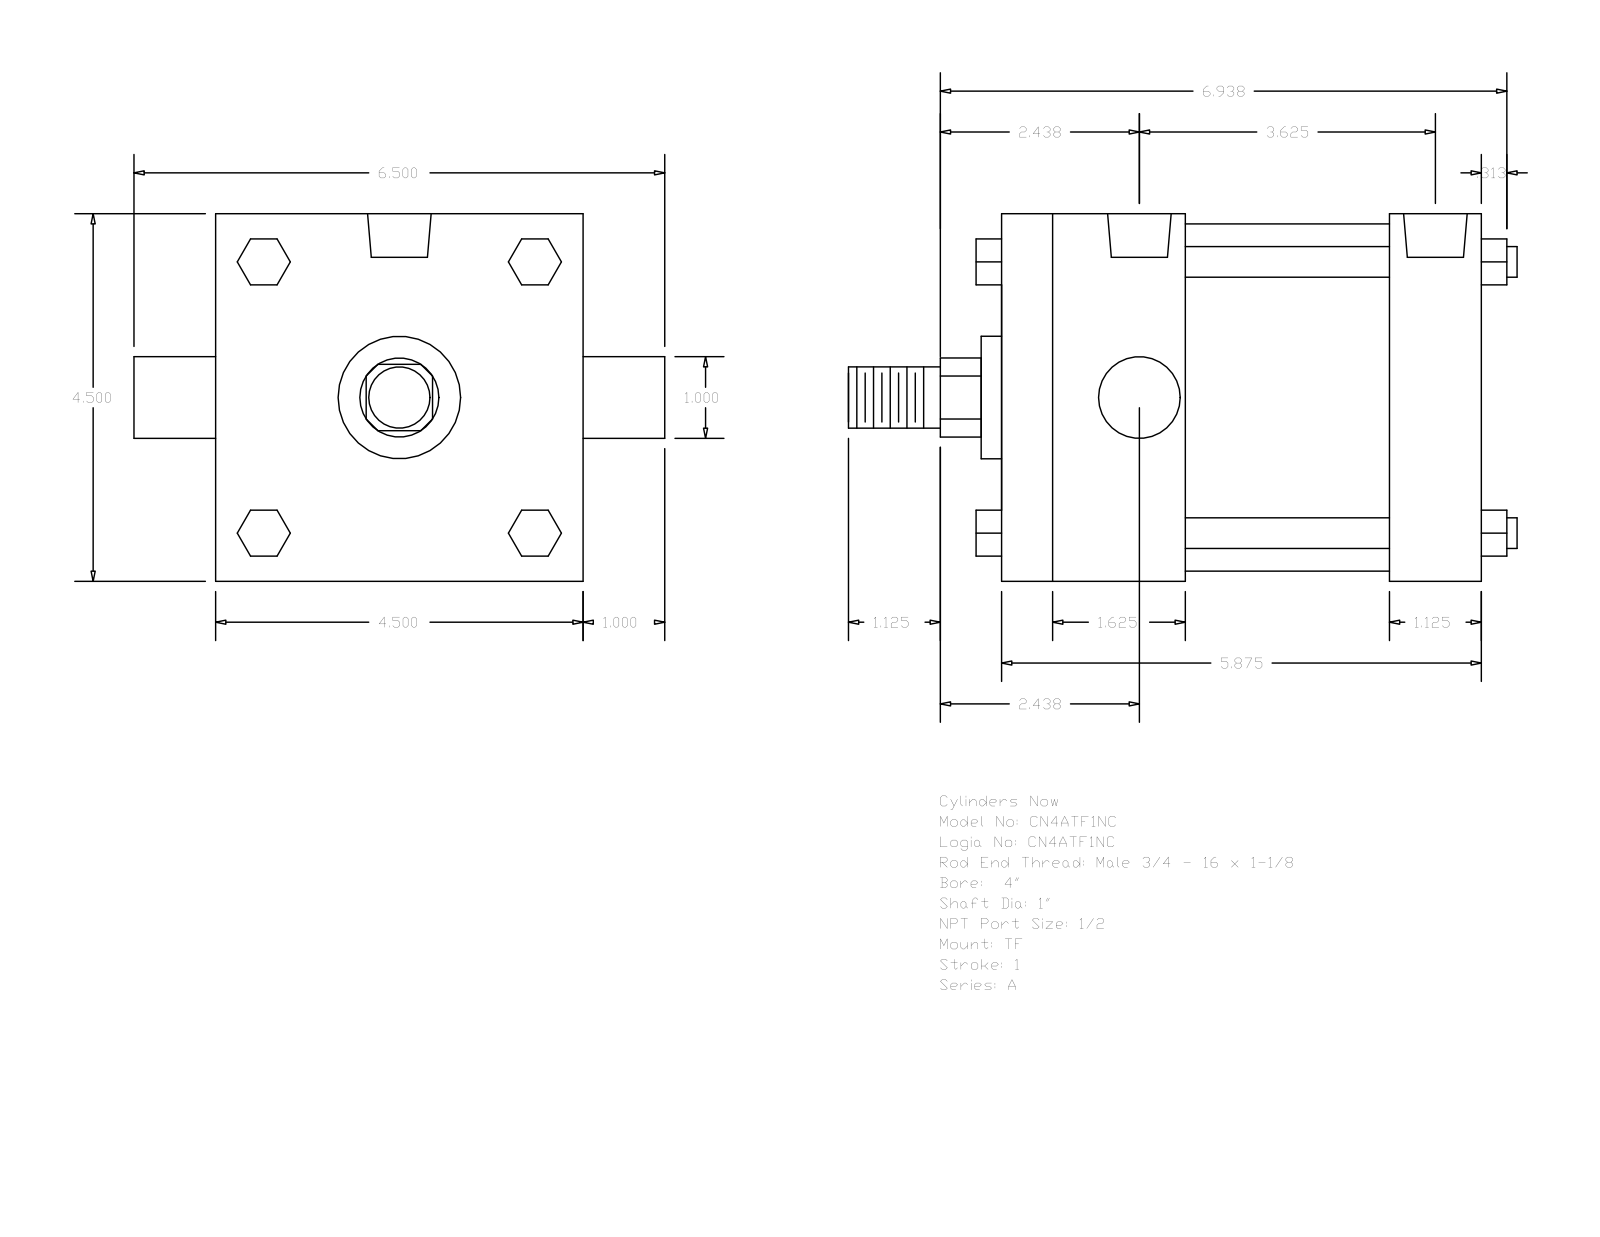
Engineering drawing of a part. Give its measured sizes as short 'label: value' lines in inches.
name: A_TF__0400_1
written by: GSSL Pune (CONFIG_CONTROL_DESIGN)
unit: in
bodies: 0 solids, 120 faces (92 planar, 28 cylindrical, 0 other)
size: 8.187 × 6.5 × 4.5
holes: 3× ⌀0.344, 2× ⌀0.778
bosses: 4× ⌀0.375, 2× ⌀1, 1× ⌀4.25, 1× ⌀1.5, 1× ⌀0.75
rounds: 1× R0.484
face distances: 4.5, 5.875, 2.5, 4.75, 1.125, 2.25, 3.625, 0.563, 5.5, 1.66
hole spacings: 0.125, 3.5, 3.375, 3.625
